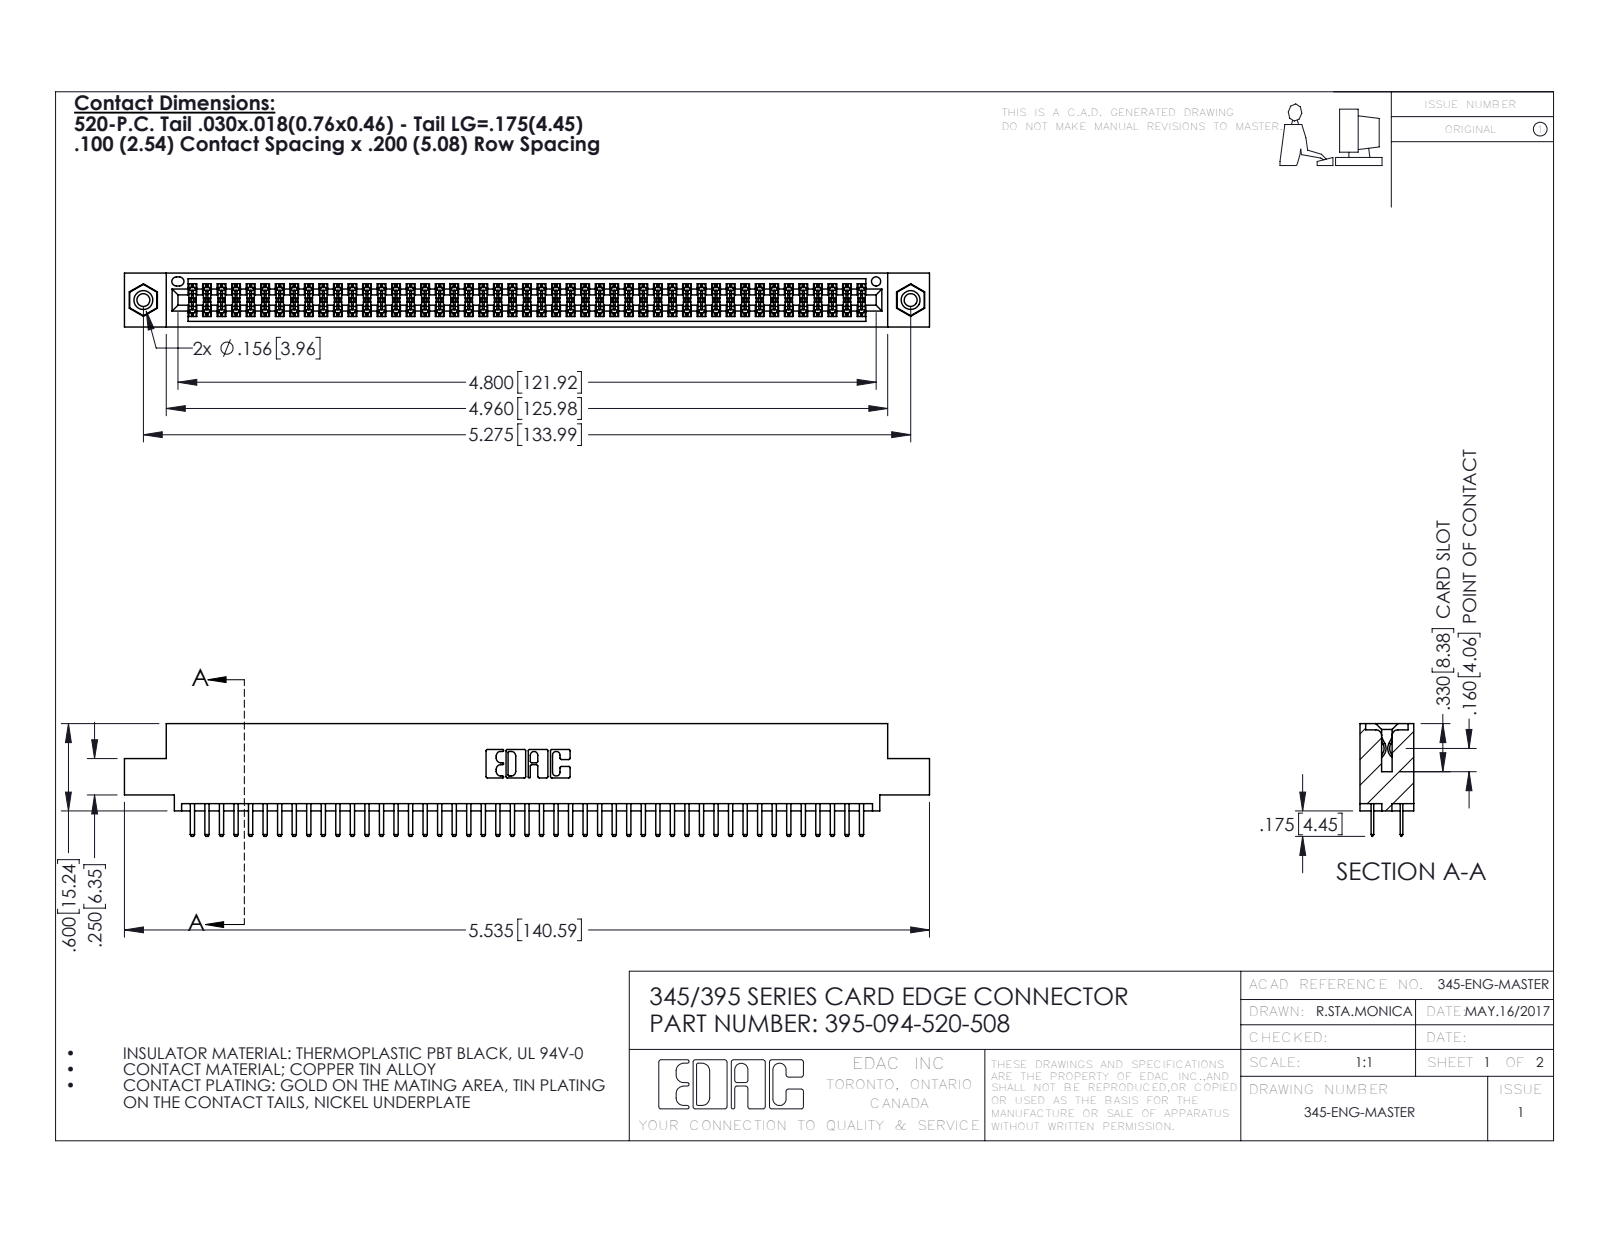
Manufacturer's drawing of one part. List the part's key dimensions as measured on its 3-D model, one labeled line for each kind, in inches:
Part name (STEP PRODUCT): 345 Part_0.110 Offset - 0.156 Dia-TI; 345-250-001_345-250-003-102; 395-094-520-508; 345-292-001_345-293-120
STEP written by: SolidWorks 2016 (CONFIG_CONTROL_DESIGN)
Units: inches
Bodies: 97 solids, 5266 faces (3406 planar, 1844 cylindrical, 16 other)
Overall size (bounding box): 5.535 × 0.775 × 0.37
Volume: 0.829 in³ · Surface area: 31.3 in²
Round holes (diameter × count): ⌀0.089 ×2, ⌀0.125 ×2, ⌀0.156 ×2, ⌀0.064 ×1
Round bosses / shafts (diameter × count): ⌀0.155 ×2
Partial cylindrical surfaces — rounded edges, fillets, slot ends (radius × count): R0.006 ×141, R0.01 ×98, R0.01 ×22, R0.007 ×6, R0.031 ×6, R0.026 ×3, R0.014 ×2, R0.019 ×2
Main face-to-face distances: 0.072, 0.298, 0.2, 0.37, 0.098, 0.272, 0.025, 0.225, 0.022, 0.072
Hole centre spacings: 0.27, 5.039, 5.275
